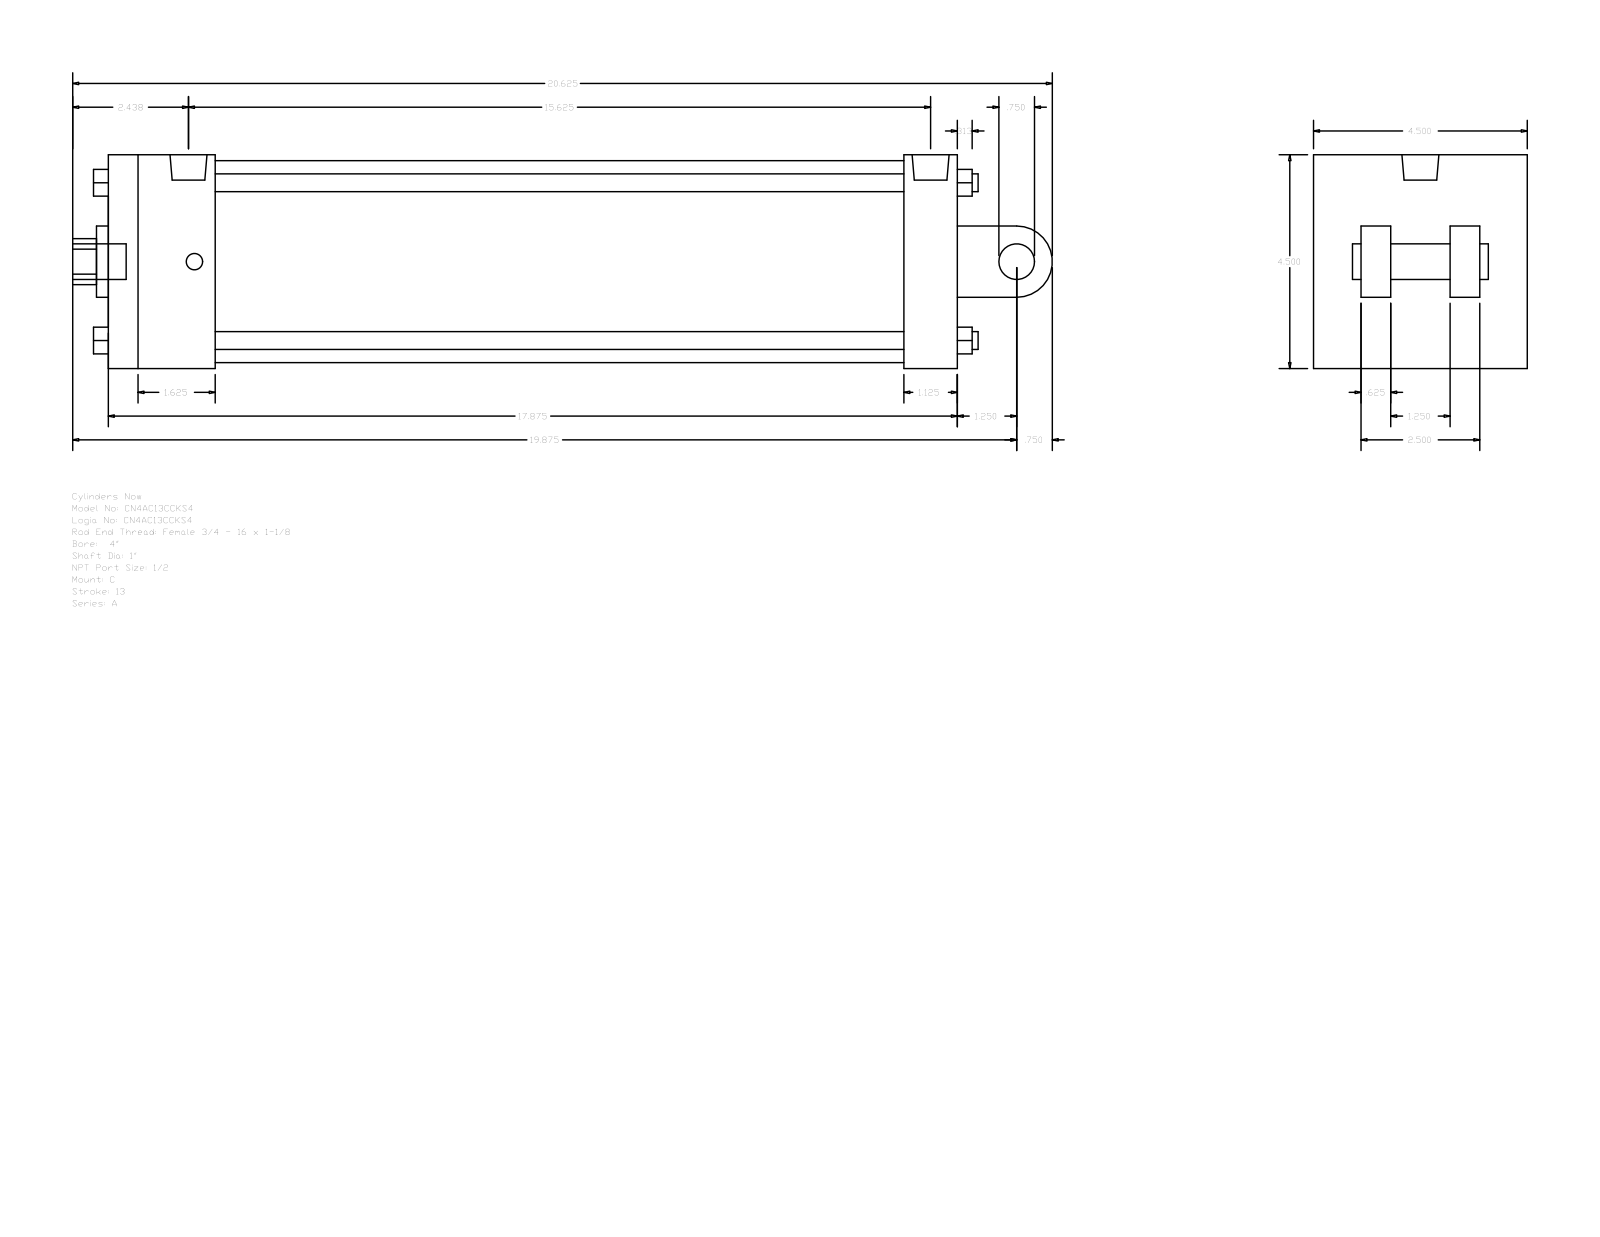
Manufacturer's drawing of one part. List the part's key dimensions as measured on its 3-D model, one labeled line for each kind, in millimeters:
Part name (STEP PRODUCT): A_C__0400_1
STEP written by: GSSL Pune (CONFIG_CONTROL_DESIGN)
Units: millimetres
Bodies: 0 solids, 135 faces (102 planar, 33 cylindrical, 0 other)
Overall size (bounding box): 523.88 × 114.3 × 114.3
Round holes (diameter × count): ⌀8.73 ×2, ⌀19.77 ×1, ⌀25.4 ×1, ⌀38.1 ×1, ⌀107.95 ×1
Round bosses / shafts (diameter × count): ⌀9.53 ×4, ⌀19.05 ×2, ⌀8.73 ×2, ⌀19.77 ×1
Partial cylindrical surfaces — rounded edges, fillets, slot ends (radius × count): R12.29 ×1, R19.05 ×1
Main face-to-face distances: 114.3, 454.02, 73.03, 28.57, 425.45, 57.15, 368.3, 396.87, 15.87, 47.63
Hole centre spacings: 3.18
